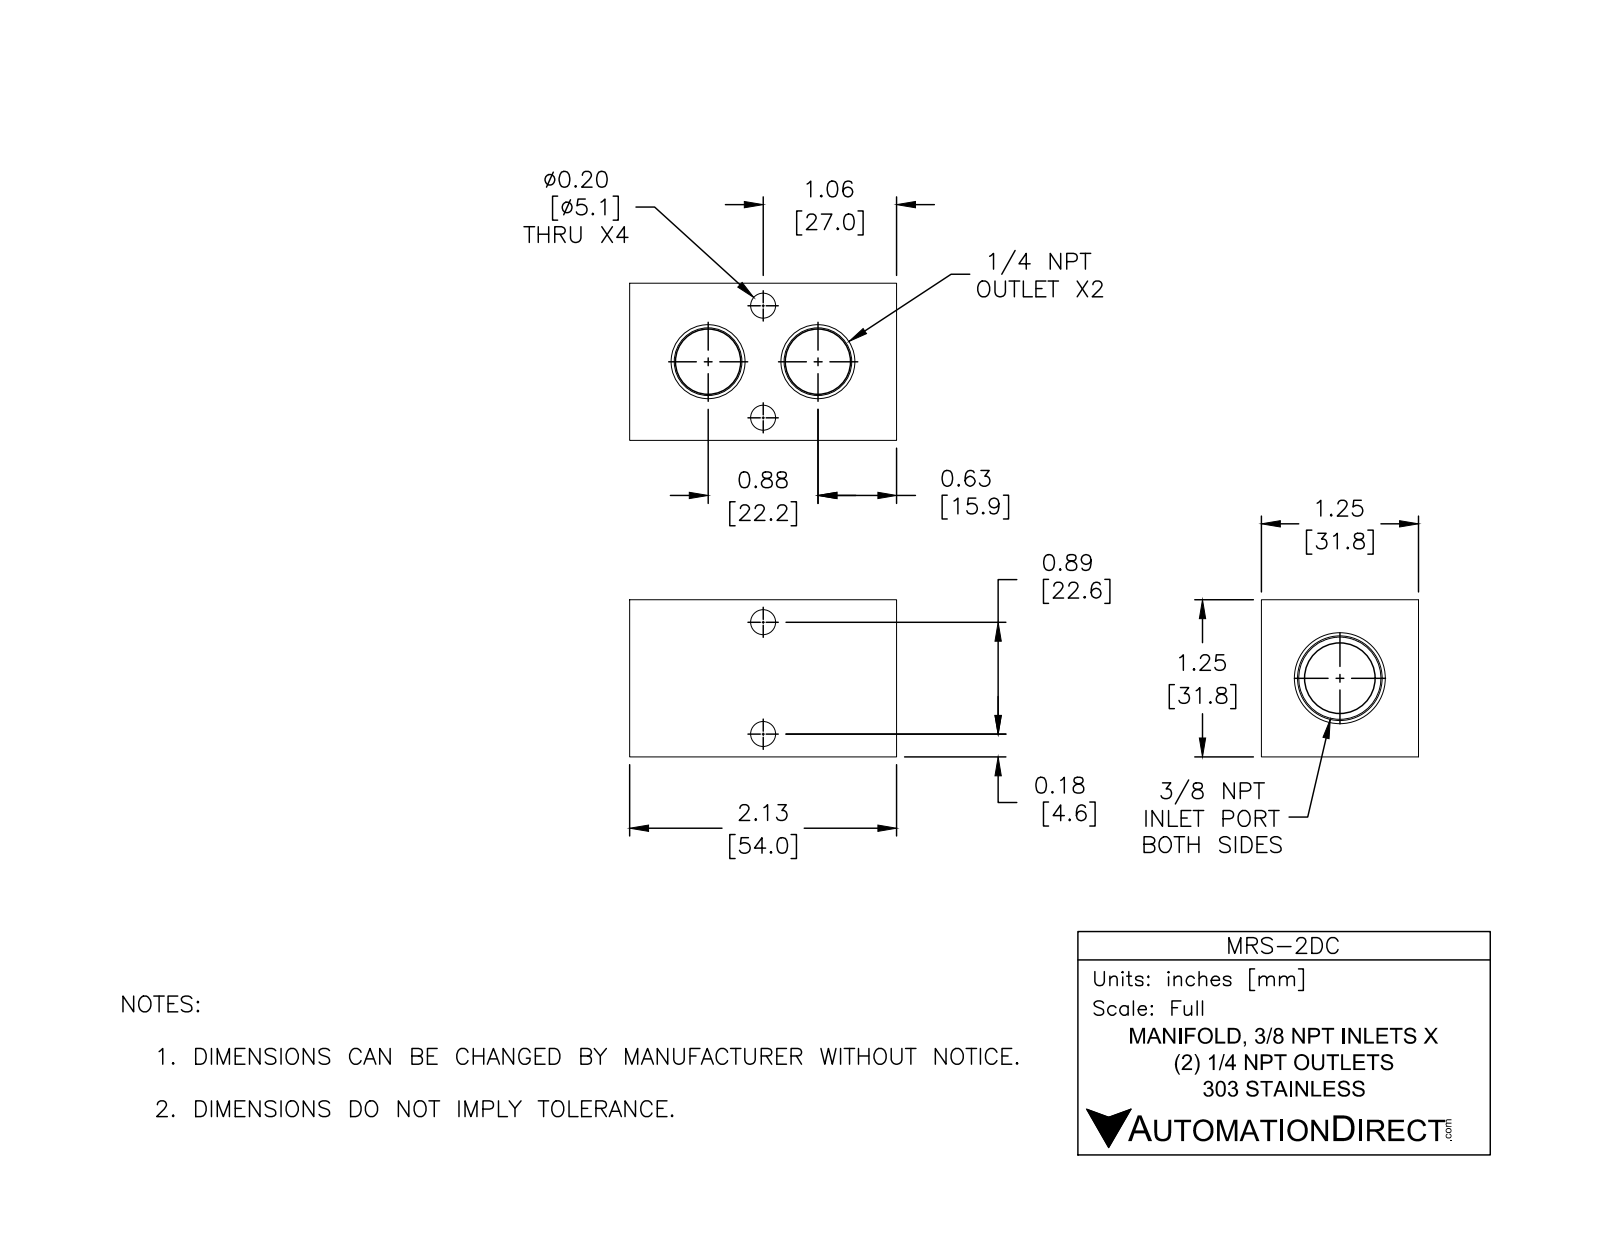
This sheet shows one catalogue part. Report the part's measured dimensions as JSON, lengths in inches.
{"part_name": "MRS-2DC", "step_written_by": "SolidWorks 2015 (CONFIG_CONTROL_DESIGN)", "units": "inches", "bodies": {"solids": 1, "faces": 58, "planar": 12, "cylindrical": 30, "other": 16}, "overall_size": [2.125, 1.25, 1.25], "volume_in3": 2.412, "surface_area_in2": 19.83, "round_holes": [[0.2, 4], [0.562, 1]], "partial_cylinders_radius": [[0.219, 2]], "face_to_face_distances": [1.25, 2.125, 0.41, 1.715, 1.305, 0.86, 0.39], "hole_center_spacings": [0.89]}
